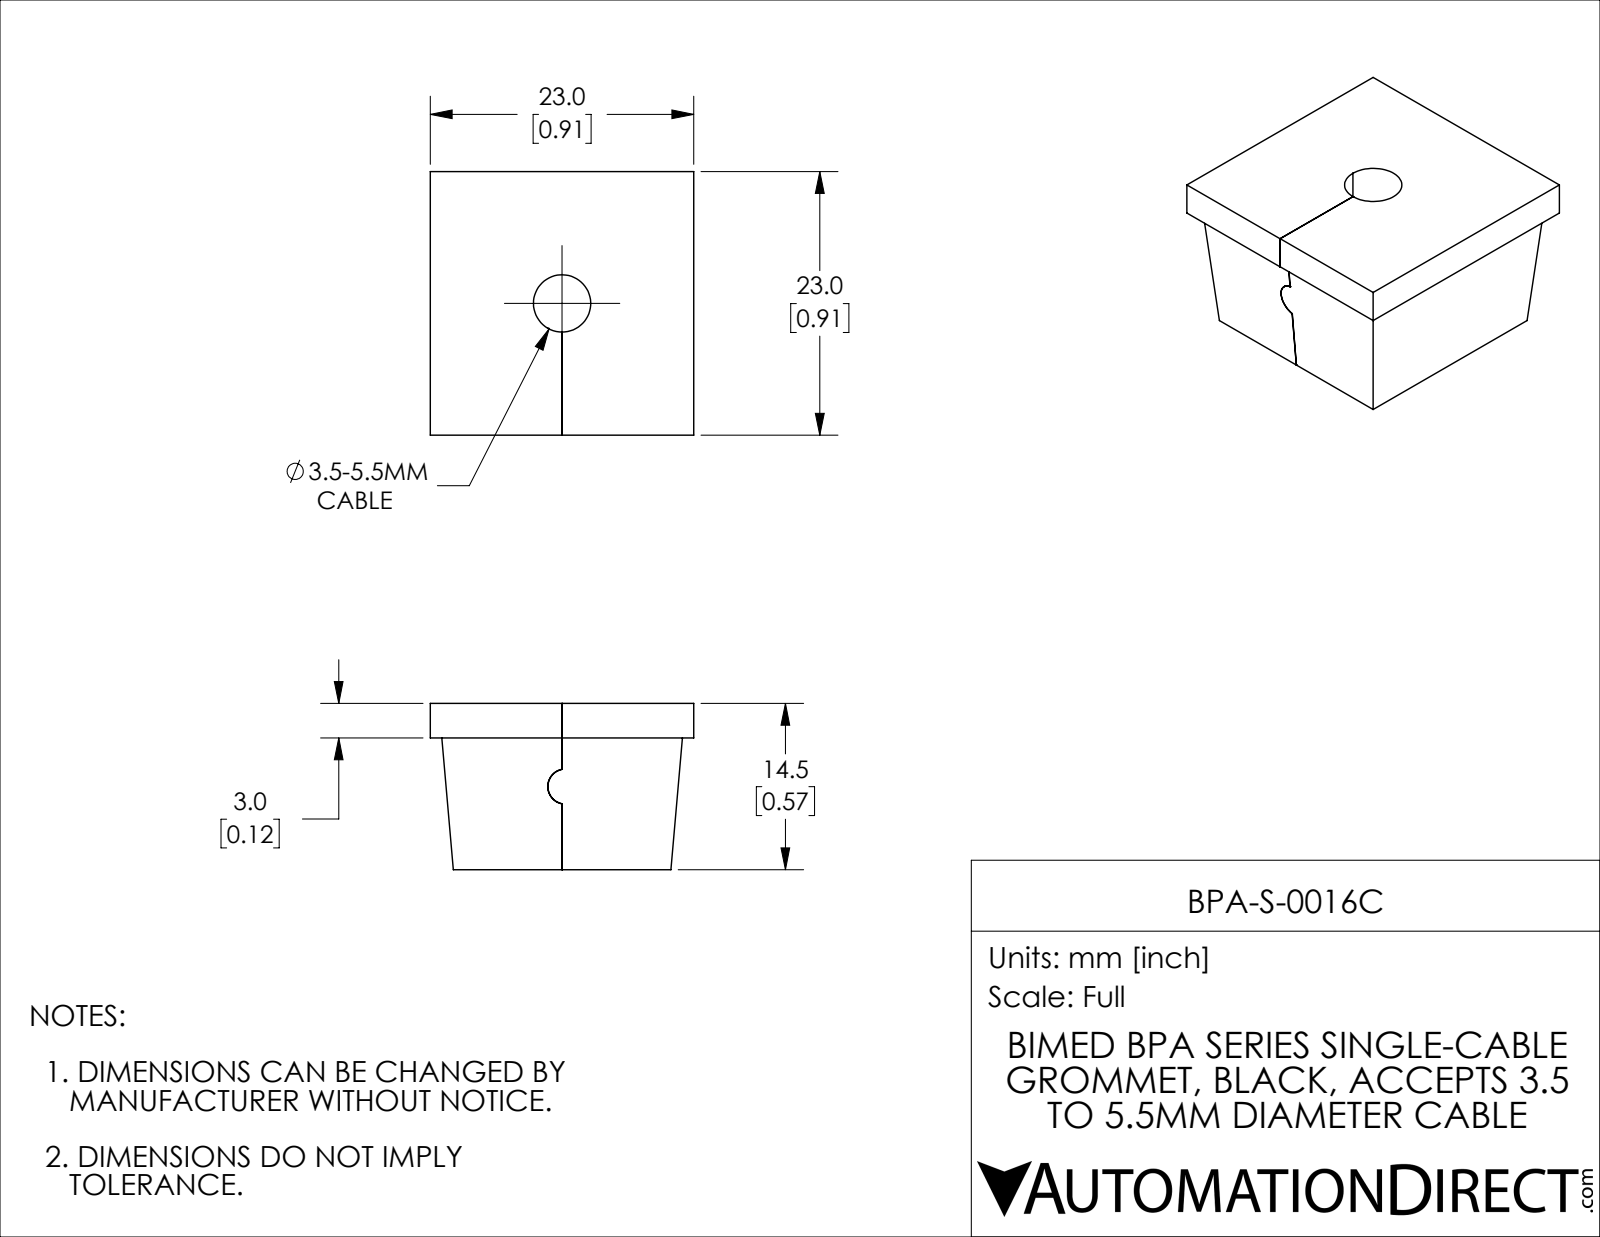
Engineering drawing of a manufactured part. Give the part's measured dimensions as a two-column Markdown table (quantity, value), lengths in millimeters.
| quantity | value |
| --- | --- |
| part name | BPA-S-0016C |
| STEP written by | SolidWorks 2021 (CONFIG_CONTROL_DESIGN) |
| units | millimeters |
| bodies | 1 solid, 22 faces (17 planar, 5 cylindrical, 0 other) |
| overall size | 23 × 23 × 14.5 |
| volume | 5 902 mm³ |
| surface area | 2 611 mm² |
| round holes (diameter × count) | 5 × 1 |
| partial cylindrical surfaces (radius × count) | 1.53 × 1, 1.54 × 1 |
| main face-to-face distances | 14.5, 11.5, 23, 3, 11.51, 11.49 |
